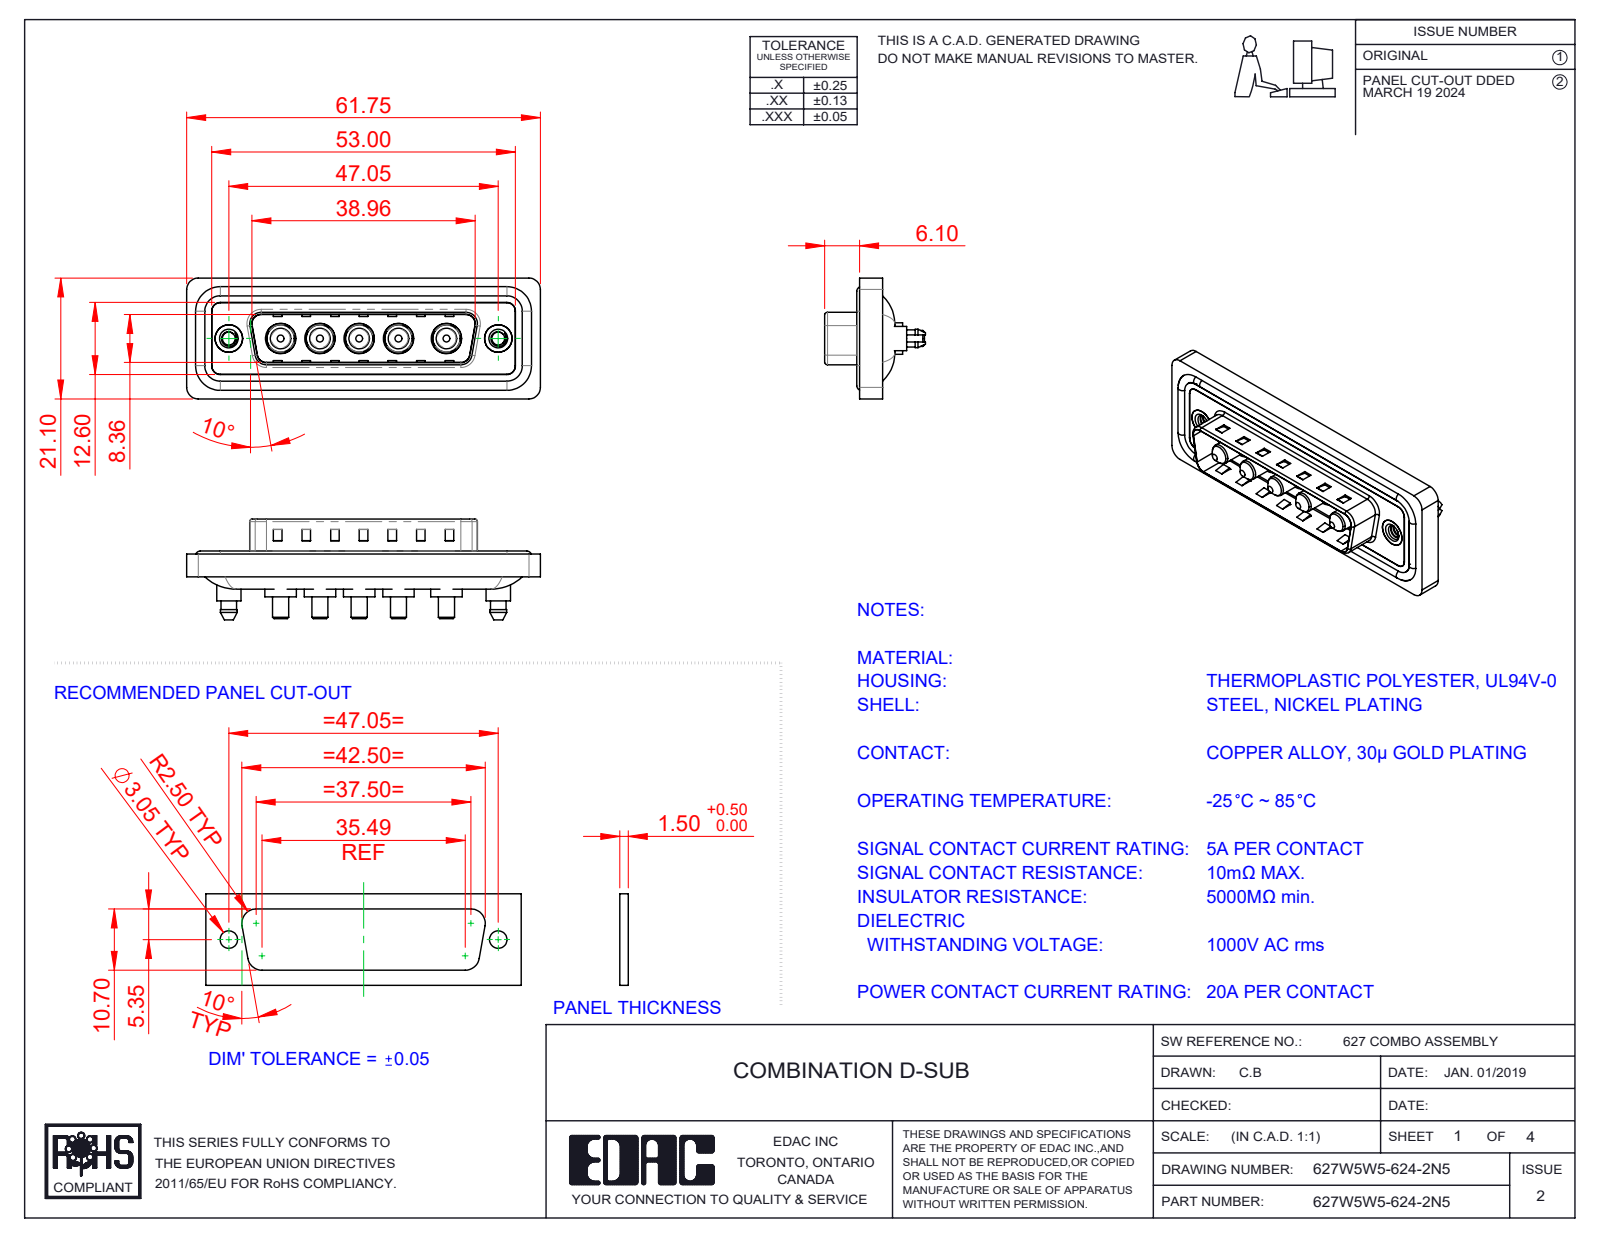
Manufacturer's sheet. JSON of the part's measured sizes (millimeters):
{"part_name": "627Combo Waterproof Housing_25 Contacts; 627Combo Housing_5W5; 627Combo Shell Front_25 Contacts; 627Combo Shell Rear_25 Contacts (+3 more)", "step_written_by": "SolidWorks 2023 (CONFIG_CONTROL_DESIGN)", "units": "millimeters", "bodies": {"solids": 17, "faces": 728, "planar": 275, "cylindrical": 315, "other": 138}, "overall_size": [61.75, 21.1, 17.6], "volume_mm3": 7606, "surface_area_mm2": 12129, "round_holes": [[4.85, 5], [5.3, 5], [2.26, 2], [4, 2], [4.8, 2], [5, 2]], "round_bosses_or_shafts": [[5.5, 5], [5.2, 5], [4.75, 5], [3.75, 5], [3.6, 5], [2.8, 5], [1.6, 4], [5.4, 2]], "partial_cylinders_radius": [[1.5, 24], [2, 18], [1.6, 10], [0.5, 8], [2.1, 5], [0.25, 4], [0.6, 4], [0.65, 4]], "face_to_face_distances": [0.4, 1.5, 3.1, 1.1, 0.5, 1.6, 2.9, 0.82, 9.58, 5.65], "hole_center_spacings": [6.86, 9.04, 13.73, 38.01, 6.87, 8.37, 8.38, 9.05]}
